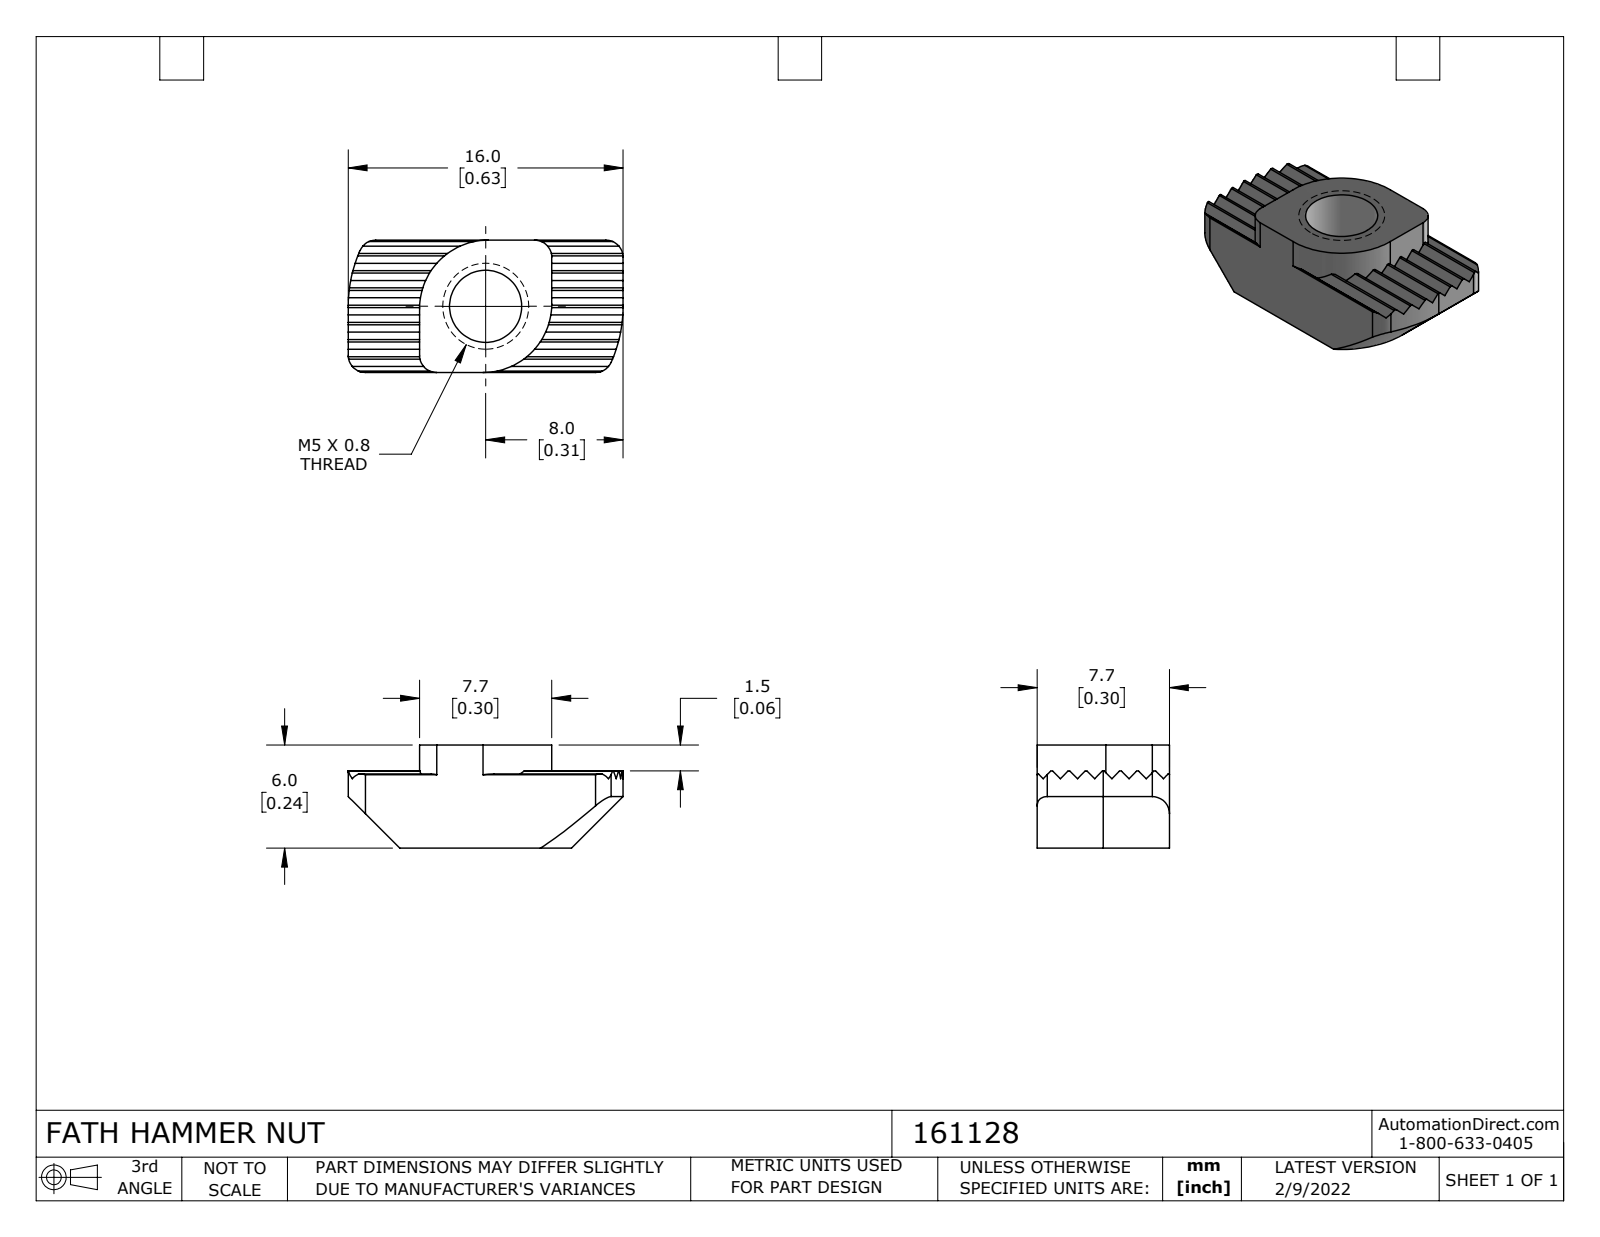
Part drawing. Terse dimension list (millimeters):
name: 161128
written by: SolidWorks 2021 (CONFIG_CONTROL_DESIGN)
unit: mm
bodies: 1 solid, 76 faces (42 planar, 32 cylindrical, 2 other)
size: 16 × 7.7 × 6
volume: 451 mm³; area: 510 mm²
holes: 1× ⌀4.2
rounds: 7× R0.1, 6× R1, 2× R4, 1× R8
face distances: 7.7, 0.71, 2.12, 1.41, 6, 2.83, 3.53, 0.7, 4.24, 1.42
